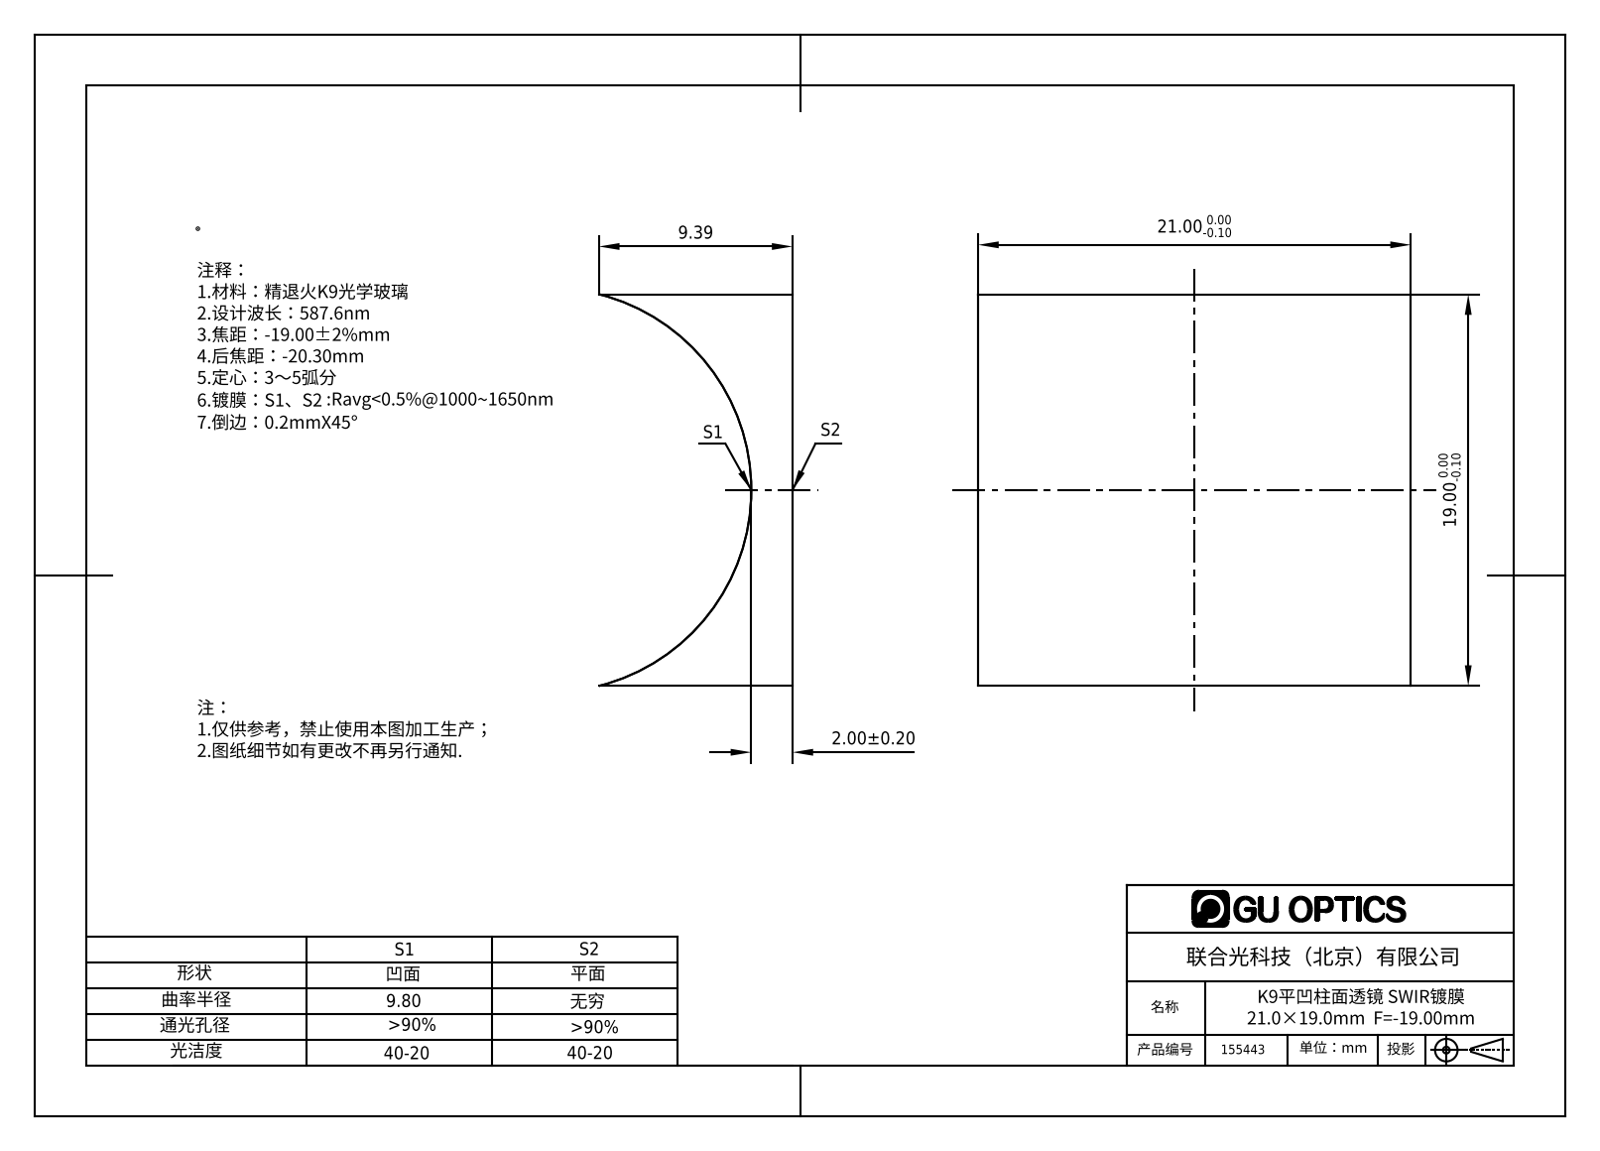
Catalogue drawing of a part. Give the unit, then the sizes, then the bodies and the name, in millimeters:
Units: millimetres
Overall size (bounding box): 21 × 19 × 9.39
Partial cylindrical surfaces — rounded edges, fillets, slot ends (radius × count): R9.8 ×1
Main face-to-face distances: 19, 21
Volume: 1 560 mm³ · Surface area: 1 487 mm²
Bodies: 1 solid, 6 faces (5 planar, 1 cylindrical, 0 other)
Part name (STEP PRODUCT): 155344
STEP written by: SolidWorks 2016 (AUTOMOTIVE_DESIGN)
